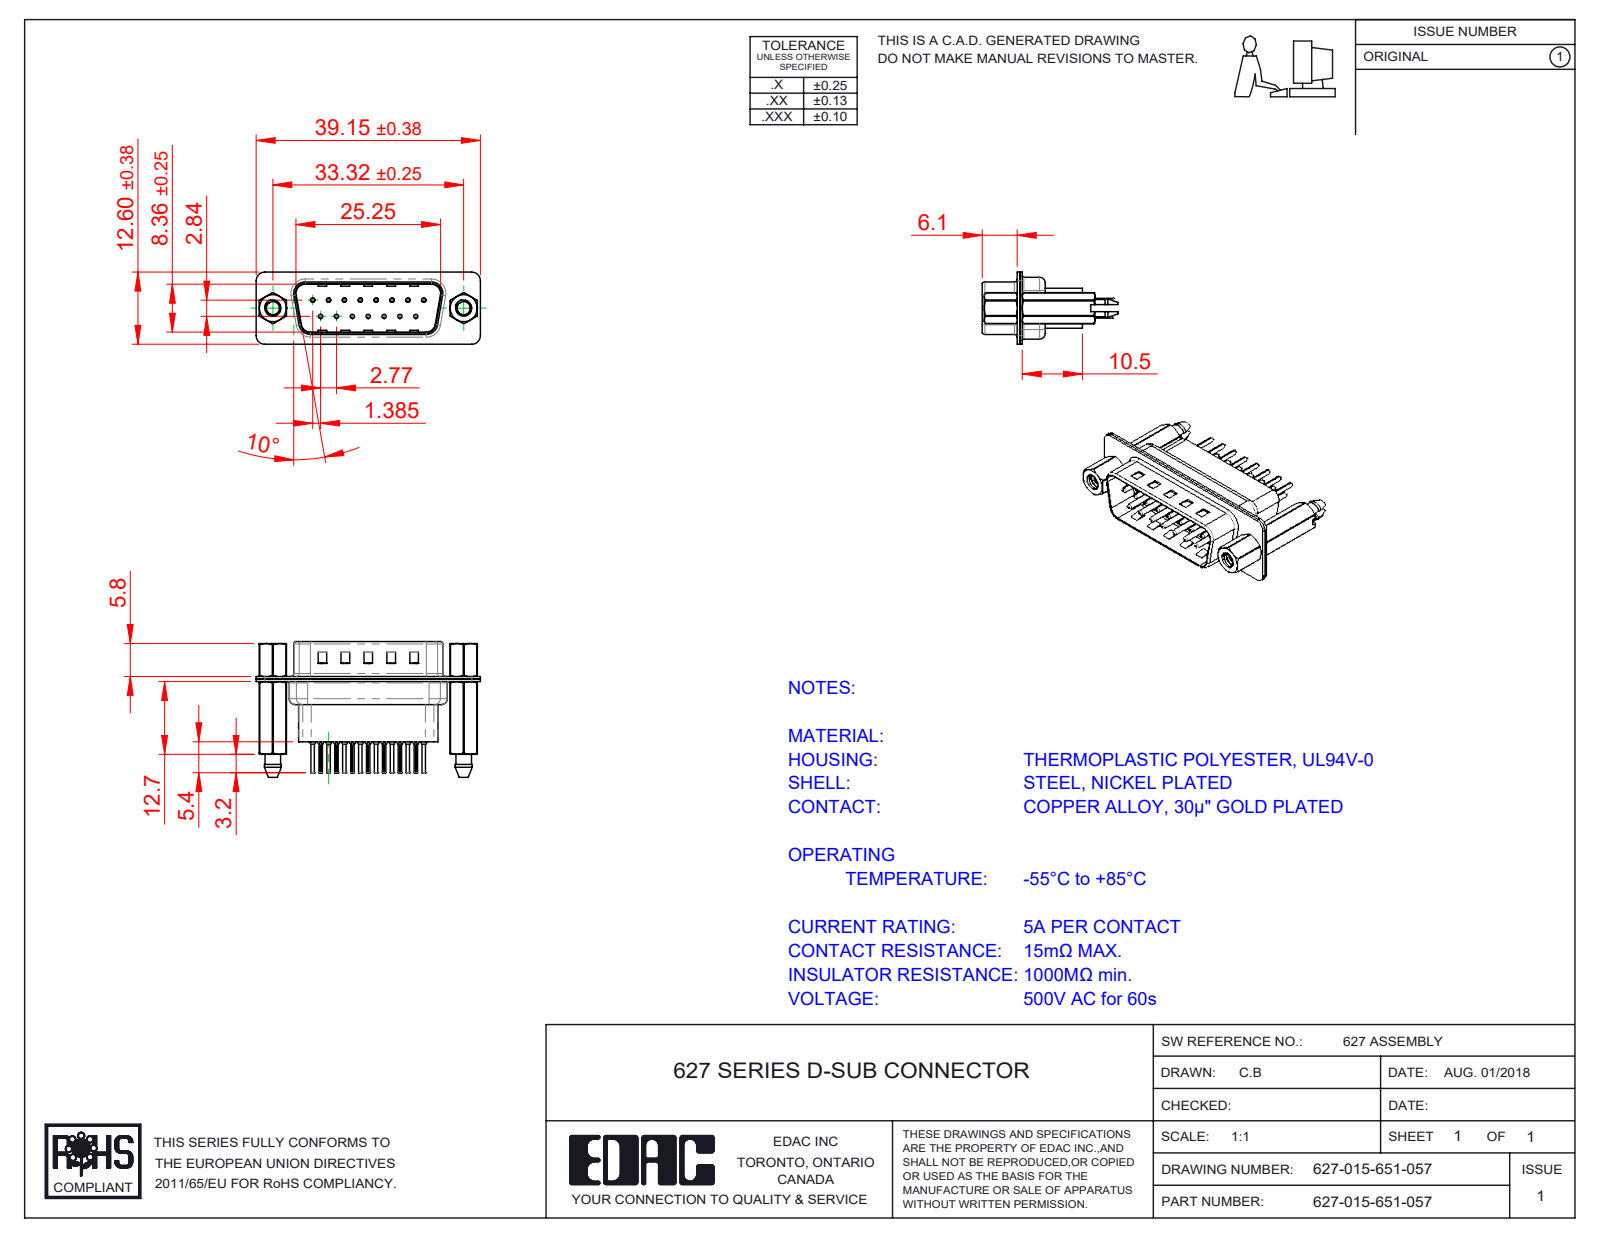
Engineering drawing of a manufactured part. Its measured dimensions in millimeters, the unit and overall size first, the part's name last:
Units: millimetres
Overall size (bounding box): 39.15 × 23.6 × 12.6
Round holes (diameter × count): ⌀0.2 ×15, ⌀0.35 ×15, ⌀1.1 ×15, ⌀1.6 ×15, ⌀2.26 ×2, ⌀2.29 ×2, ⌀4 ×2, ⌀4.8 ×2
Round bosses / shafts (diameter × count): ⌀2 ×15, ⌀1.5 ×15, ⌀0.75 ×15, ⌀0.6 ×15, ⌀4.9 ×2, ⌀2.79 ×2
Partial cylindrical surfaces — rounded edges, fillets, slot ends (radius × count): R0.1 ×30, R1.5 ×18, R2 ×12, R1.6 ×10, R0.5 ×8, R0.25 ×4, R0.6 ×4, R0.65 ×4
Main face-to-face distances: 0.4, 0.45, 4.76, 0.9, 0.82, 9.58, 1.5, 0.68, 7.68, 1.4
Hole centre spacings: 3.16, 2.77, 5.54, 8.31, 11.08, 5.03, 5.04, 7.48
Volume: 3 070 mm³ · Surface area: 7 852 mm²
Bodies: 22 solids, 2044 faces (553 planar, 826 cylindrical, 665 other)
Part name (STEP PRODUCT): 627 Shell Front_15 Contacts; 627 Shell Rear_15 Contacts; 627 Contact Row 2_41; 627-015-651-057 (+4 more)
STEP written by: SolidWorks 2020 (CONFIG_CONTROL_DESIGN)
